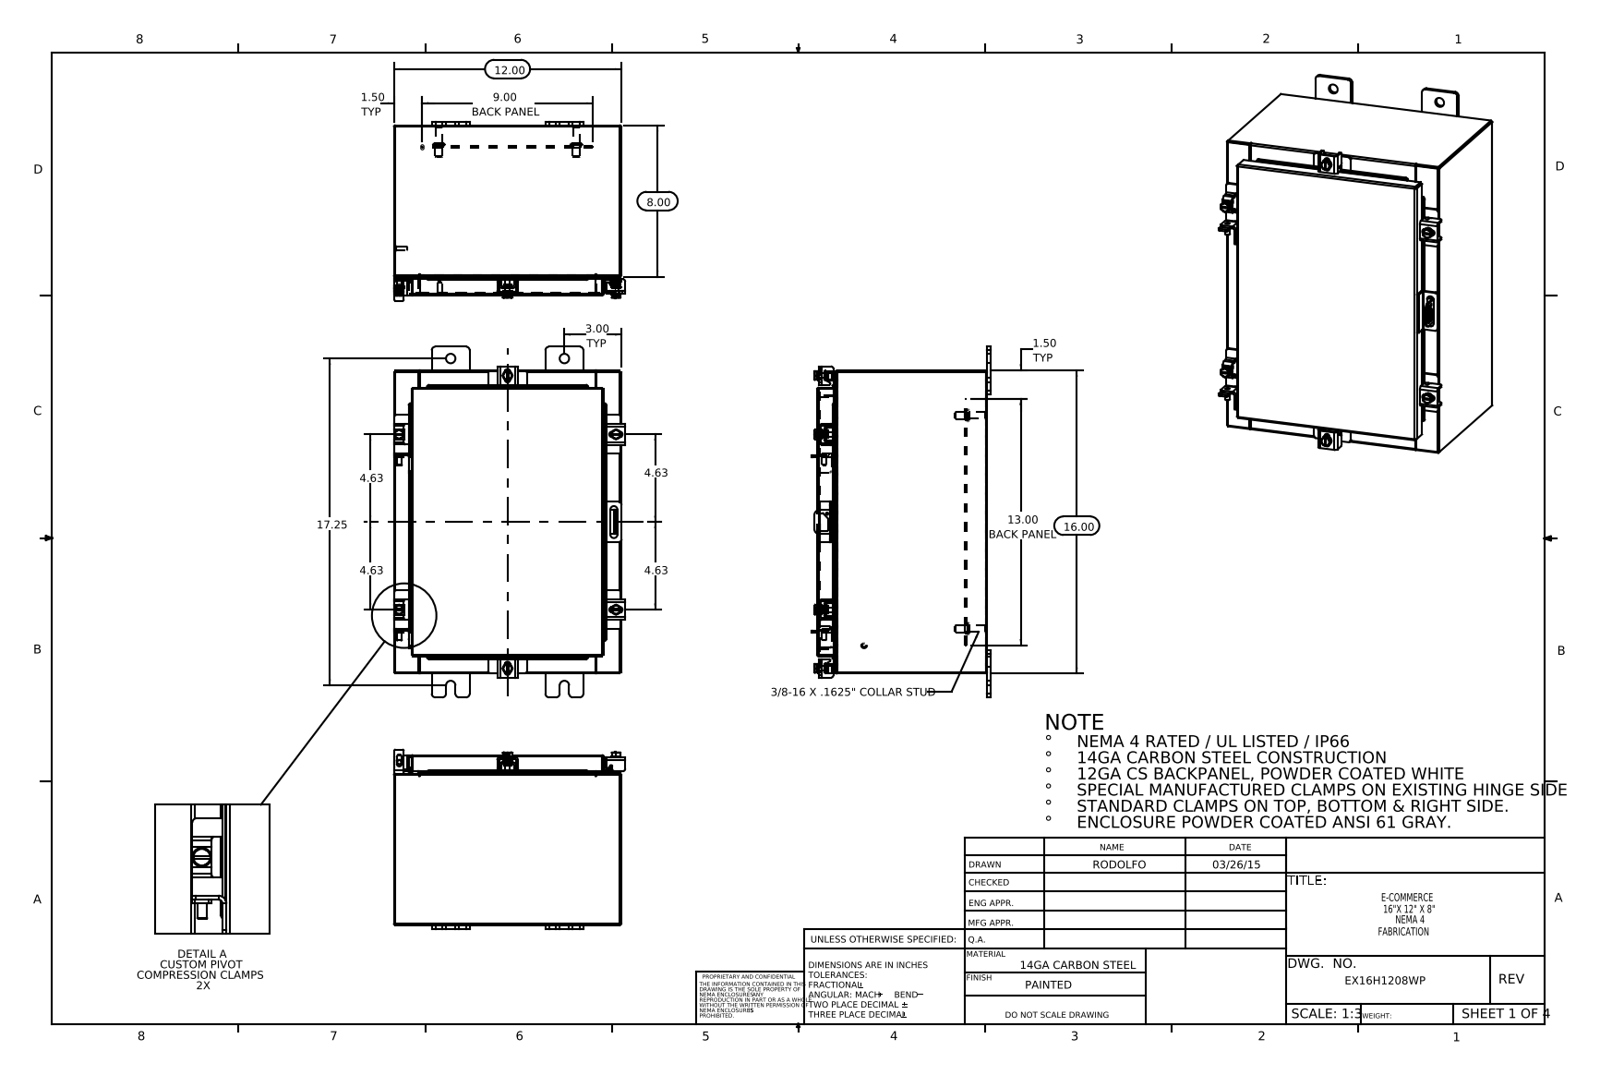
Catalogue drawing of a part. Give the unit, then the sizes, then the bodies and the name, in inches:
Units: inches
Overall size (bounding box): 18.5 × 12.211 × 9.453
Round holes (diameter × count): ⌀0.5 ×8, ⌀0.213 ×6, ⌀0.26 ×6, ⌀0.125 ×1, ⌀0.25 ×1
Round bosses / shafts (diameter × count): ⌀0.5 ×6, ⌀0.25 ×6, ⌀0.625 ×4, ⌀0.399 ×4, ⌀0.375 ×4, ⌀0.33 ×4, ⌀0.315 ×2, ⌀0.236 ×2
Partial cylindrical surfaces — rounded edges, fillets, slot ends (radius × count): R0.06 ×26, R0.19 ×24, R0.013 ×22, R0.088 ×22, R0.1 ×16, R0.09 ×12, R0.12 ×10, R0.125 ×10
Main face-to-face distances: 0.075, 8.9, 11.925, 15.925, 8.975, 8.826, 7.925, 0.975, 11.85, 1
Hole centre spacings: 13.834, 6.511, 9.404, 10.463, 13.613, 1.858, 2.326, 2.327
Volume: 88.8 in³ · Surface area: 2 252 in²
Bodies: 49 solids, 1234 faces (671 planar, 451 cylindrical, 112 other)
Part name (STEP PRODUCT): EX16H1208WP Top; EX16H1208WP Clamp Bracket; Clamp Top_RTP31; EX16H1208WP Backpanel (+8 more)
STEP written by: SolidWorks 2014 (CONFIG_CONTROL_DESIGN)
